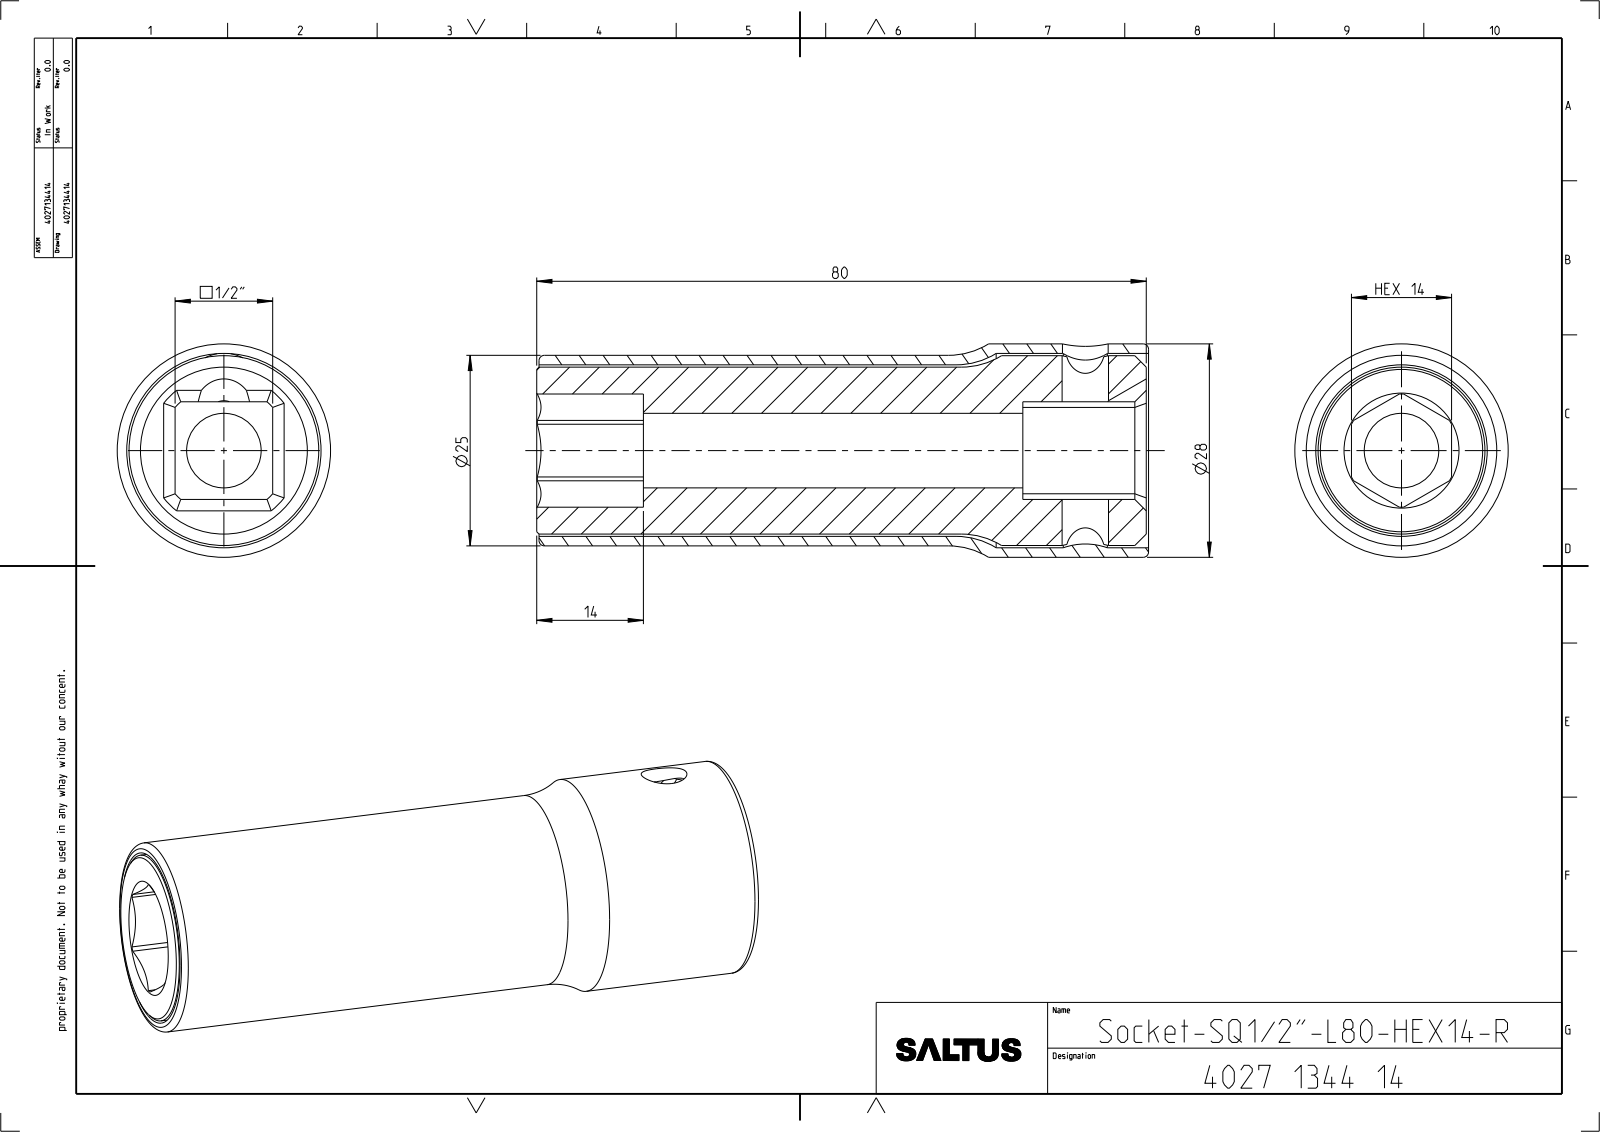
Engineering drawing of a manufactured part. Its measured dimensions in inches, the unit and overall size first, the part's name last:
Units: inches
Overall size (bounding box): 3.161 × 1.102 × 1.102
Round holes (diameter × count): ⌀0.236 ×1, ⌀0.24 ×1, ⌀0.401 ×1, ⌀0.886 ×1, ⌀1.004 ×1
Round bosses / shafts (diameter × count): ⌀1.102 ×1, ⌀0.984 ×1, ⌀0.98 ×1, ⌀0.862 ×1
Partial cylindrical surfaces — rounded edges, fillets, slot ends (radius × count): R0.157 ×1, R0.315 ×1, R0.337 ×1
Main face-to-face distances: 0.557, 0.505, 0.026, 0.531, 3.15, 2.598, 0.551, 0.638, 1.961, 2.512
Volume: 1.848 in³ · Surface area: 34.13 in²
Bodies: 2 solids, 79 faces (21 planar, 35 cylindrical, 23 other)
Part name (STEP PRODUCT): 4027130314; 4027299275; 4027134414_ASM
STEP written by: CREO PARAMETRIC BY PTC INC, 2022414 (CONFIG_CONTROL_DESIGN)
